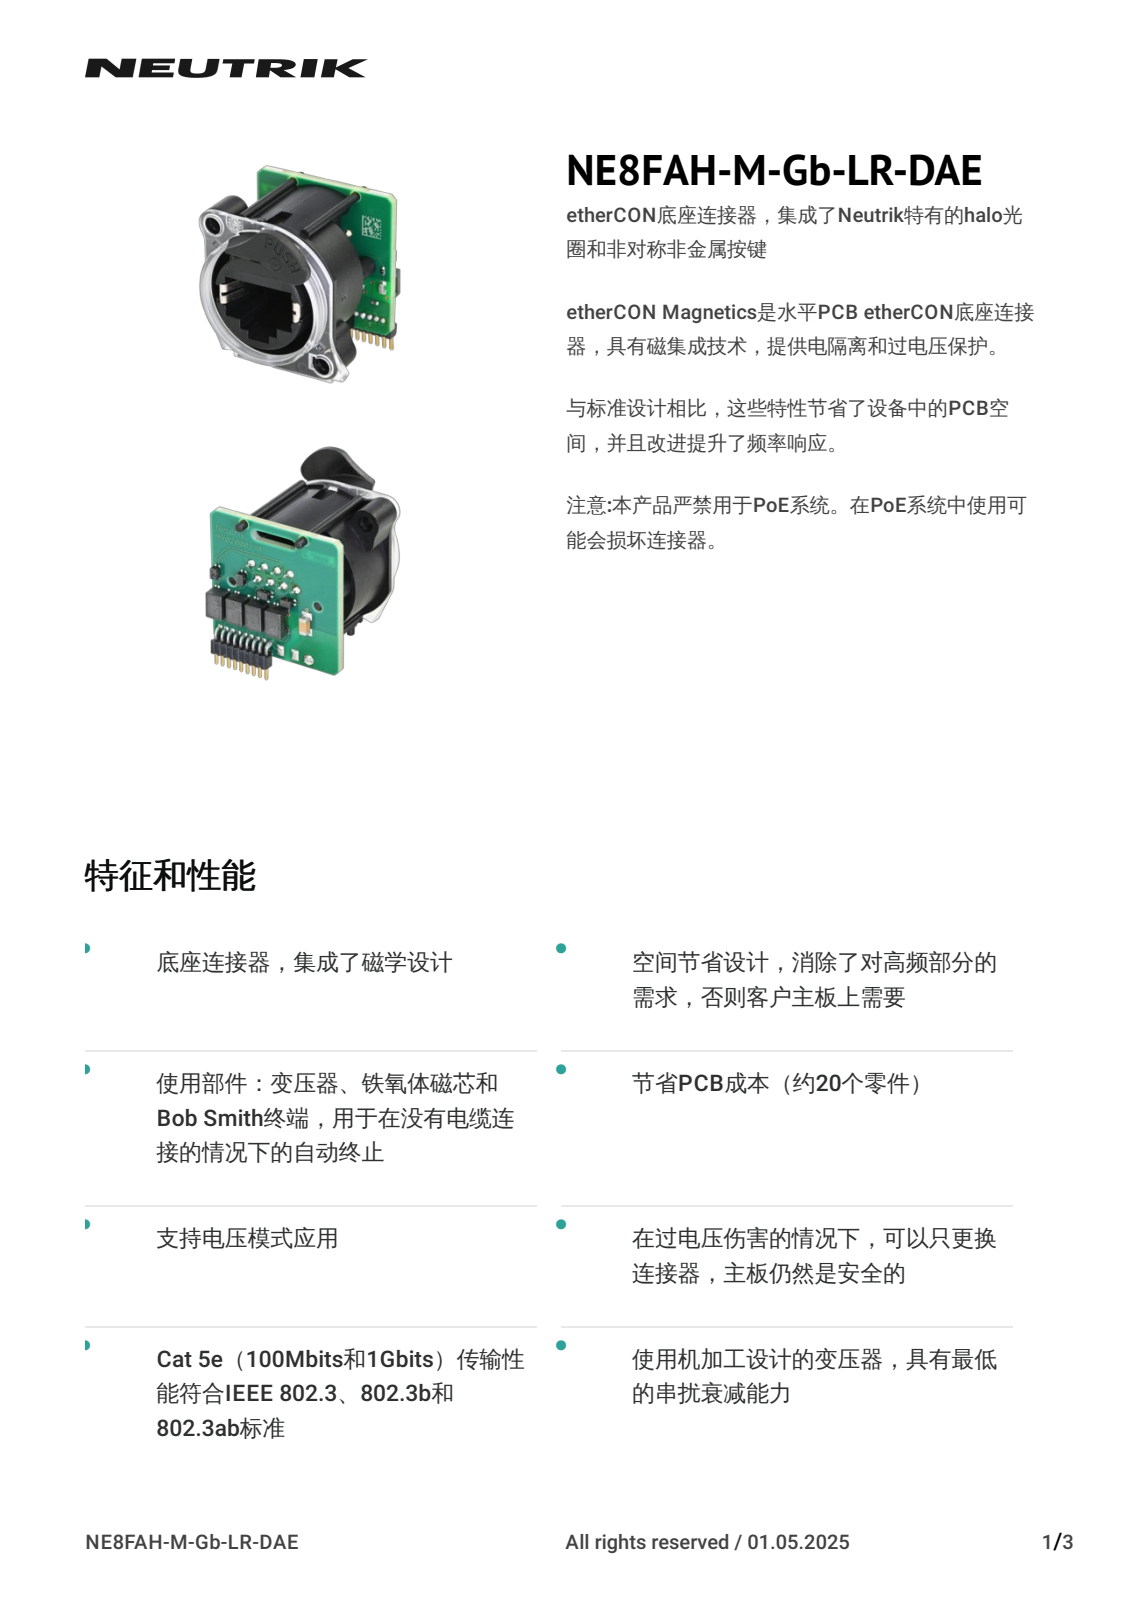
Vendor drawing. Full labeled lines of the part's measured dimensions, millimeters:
Part name (STEP PRODUCT): NE8FAH-M-MB-LR-DAE
STEP written by: CREO PARAMETRIC BY PTC INC, 2021184 (CONFIG_CONTROL_DESIGN)
Units: millimetres
Bodies: 16 solids, 1942 faces (1172 planar, 407 cylindrical, 363 other)
Overall size (bounding box): 31.02 × 30.7 × 26.39
Volume: 9 318 mm³ · Surface area: 7 950 mm²
Round holes (diameter × count): ⌀0.6 ×8, ⌀0.8 ×8, ⌀1.7 ×4, ⌀1.35 ×2, ⌀2.4 ×2, ⌀3 ×2, ⌀1.2 ×1, ⌀2.13 ×1
Round bosses / shafts (diameter × count): ⌀0.51 ×9, ⌀1.5 ×6, ⌀3 ×2, ⌀22 ×1, ⌀20.5 ×1
Partial cylindrical surfaces — rounded edges, fillets, slot ends (radius × count): R0.2 ×60, R0.1 ×56, R0.25 ×18, R0.35 ×12, R1 ×10, R0.3 ×9, R5 ×7, R0.6 ×6
Main face-to-face distances: 2.4, 19.7, 17.3, 1.2, 1, 20.9, 18.5, 0.9, 10.9, 10
Hole centre spacings: 2.54, 5.08, 1.27, 2.84, 3.81, 4.58, 6.84, 7.62
